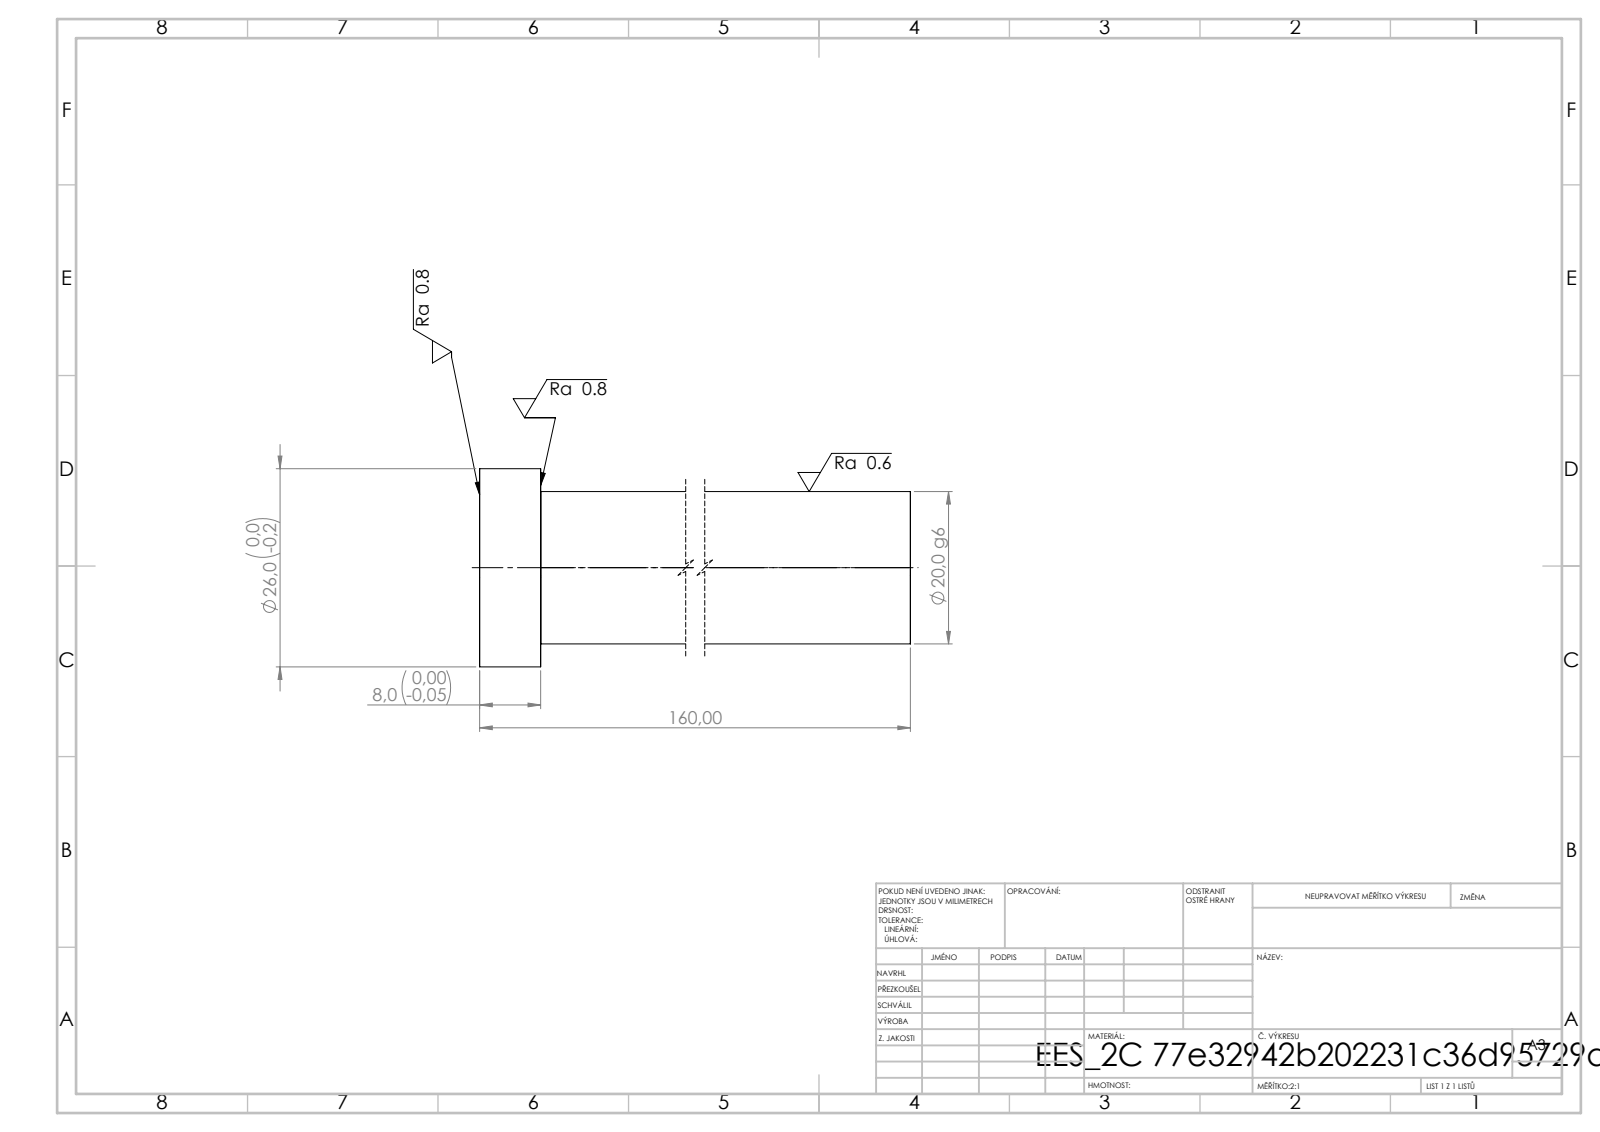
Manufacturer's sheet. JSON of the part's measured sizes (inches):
{"step_written_by": "SolidWorks 2019 (CONFIG_CONTROL_DESIGN)", "units": "inches", "bodies": {"solids": 1, "faces": 7, "planar": 3, "cylindrical": 4, "other": 0}, "overall_size": [6.299, 1.024, 1.024], "volume_in3": 3.173, "surface_area_in2": 17.46, "round_bosses_or_shafts": [[1.024, 1], [0.787, 1]], "face_to_face_distances": [6.299, 0.315, 5.984]}
